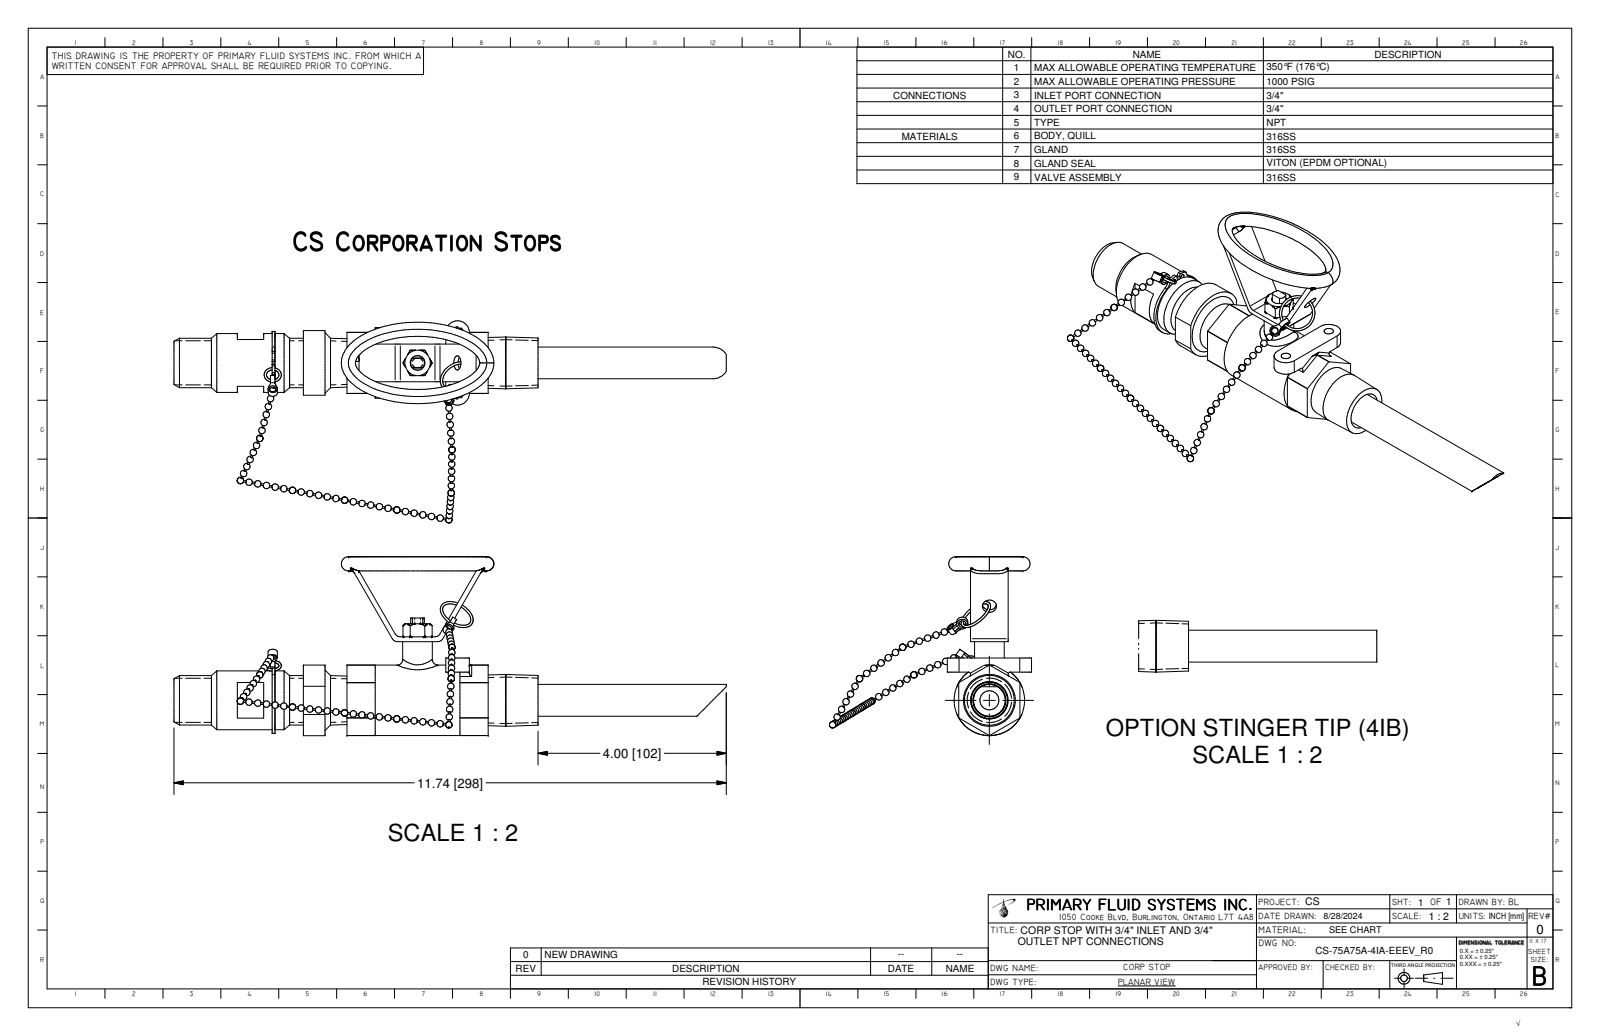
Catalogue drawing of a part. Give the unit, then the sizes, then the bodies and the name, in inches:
Units: inches
Overall size (bounding box): 11.736 × 4.294 × 3.8
Round holes (diameter × count): ⌀0.098 ×2, ⌀0.15 ×2, ⌀0.157 ×2, ⌀0.2 ×2, ⌀0.3 ×1, ⌀0.313 ×1, ⌀0.403 ×1, ⌀0.423 ×1, ⌀0.697 ×1, ⌀0.788 ×1, ⌀0.793 ×1, ⌀0.803 ×1
Round bosses / shafts (diameter × count): ⌀0.035 ×9, ⌀0.236 ×2, ⌀1.498 ×1, ⌀1.343 ×1, ⌀1.25 ×1, ⌀1.14 ×1, ⌀1.05 ×1, ⌀0.675 ×1
Partial cylindrical surfaces — rounded edges, fillets, slot ends (radius × count): R0.125 ×8, R0.05 ×6, R0.054 ×2, R0.098 ×2, R0.197 ×2, R0.25 ×2, R0.145 ×1, R0.75 ×1
Main face-to-face distances: 0.104, 1.3, 0.25, 0.926, 0.3, 3.926, 1.05, 0.152, 1.148, 0.098
Hole centre spacings: 0.657, 1.067, 0.252, 0.314, 0.54, 0.707, 0.91, 1.29
Volume: 10.58 in³ · Surface area: 115.7 in²
Bodies: 21 solids, 349 faces (139 planar, 114 cylindrical, 96 other)
STEP written by: Autodesk Inventor 2025 (CONFIG_CONTROL_DESIGN)
